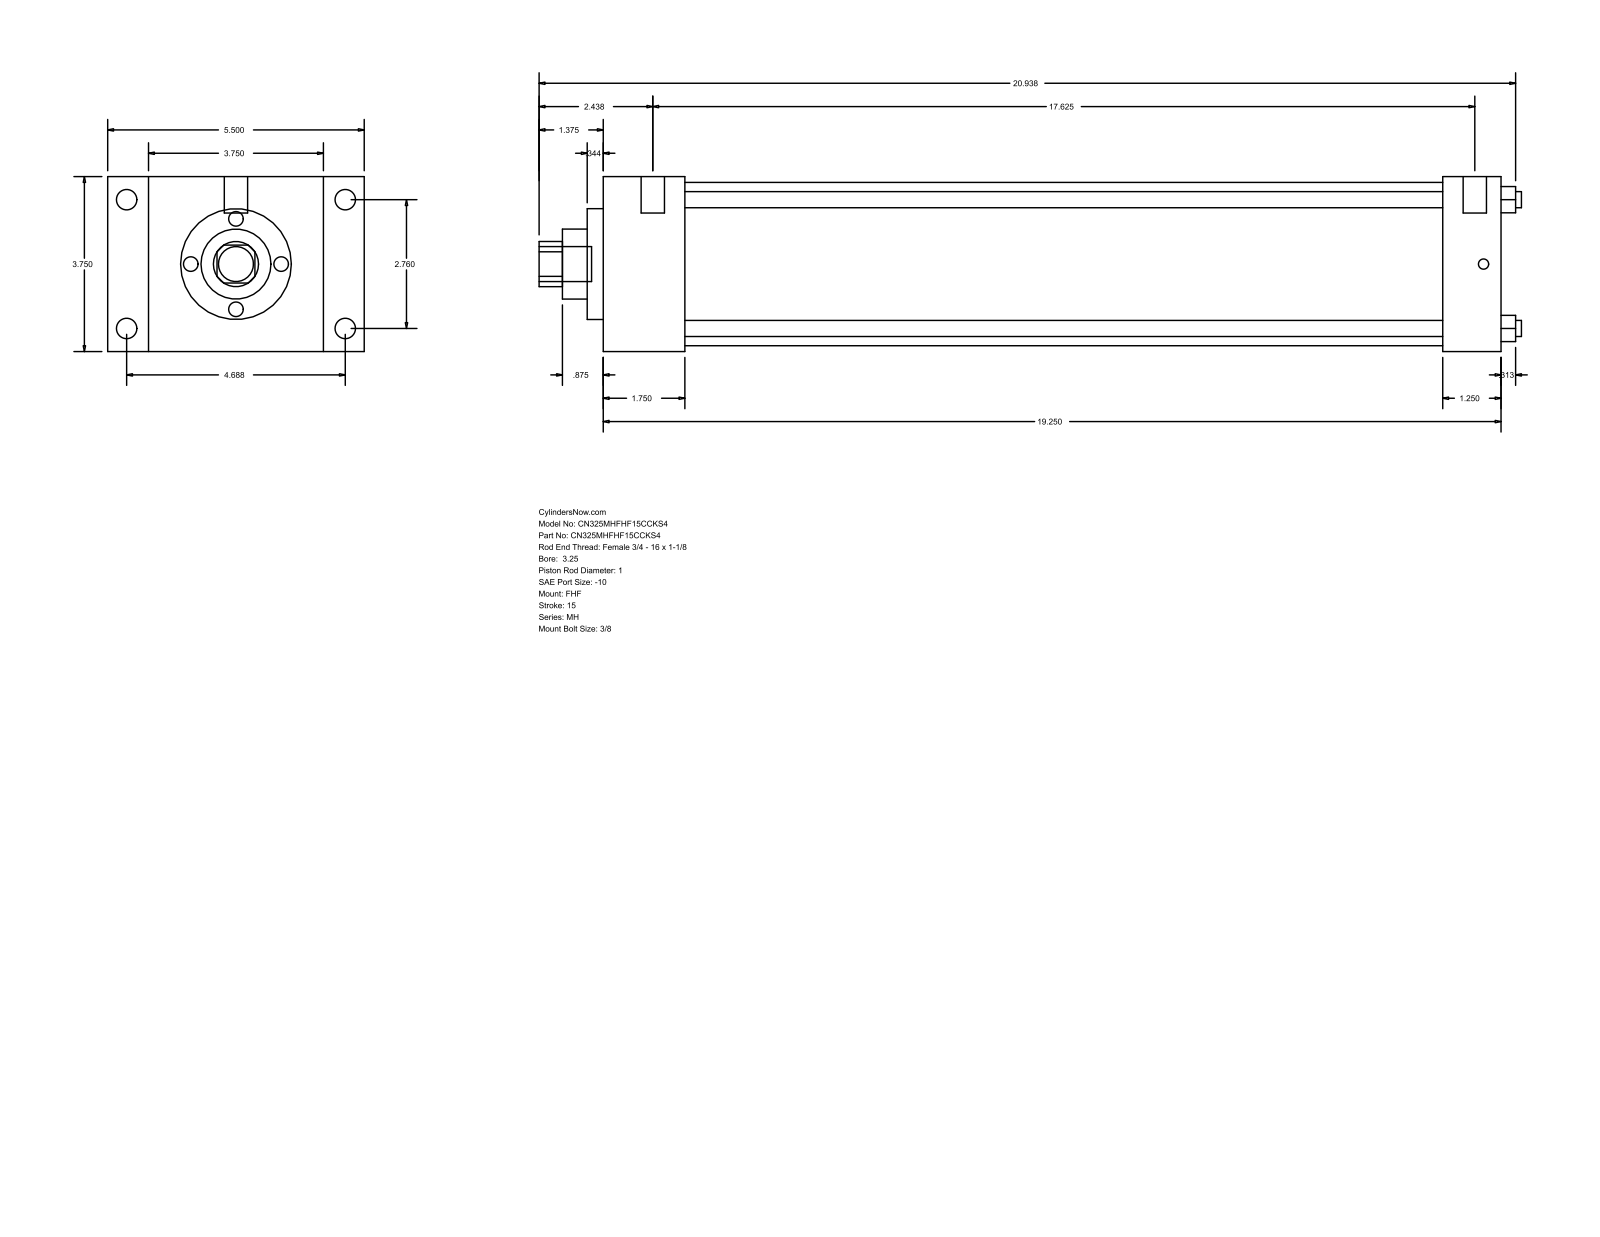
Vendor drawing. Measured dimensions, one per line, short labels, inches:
name: MH_FHF__0325_1
written by: GSSL Pune (CONFIG_CONTROL_DESIGN)
unit: in
bodies: 0 solids, 90 faces (61 planar, 29 cylindrical, 0 other)
size: 21.063 × 5.5 × 3.75
holes: 4× ⌀0.345, 1× ⌀1, 1× ⌀1.5, 1× ⌀2.375, 1× ⌀3.5
bosses: 4× ⌀0.438, 4× ⌀0.219, 2× ⌀0.5, 1× ⌀0.75
rounds: 1× R0.484
face distances: 3.75, 19.25, 1.75, 17.5, 0.875, 4.625, 5.5, 18, 16.25, 1.25
hole spacings: 1.952, 2.76, 3.903
